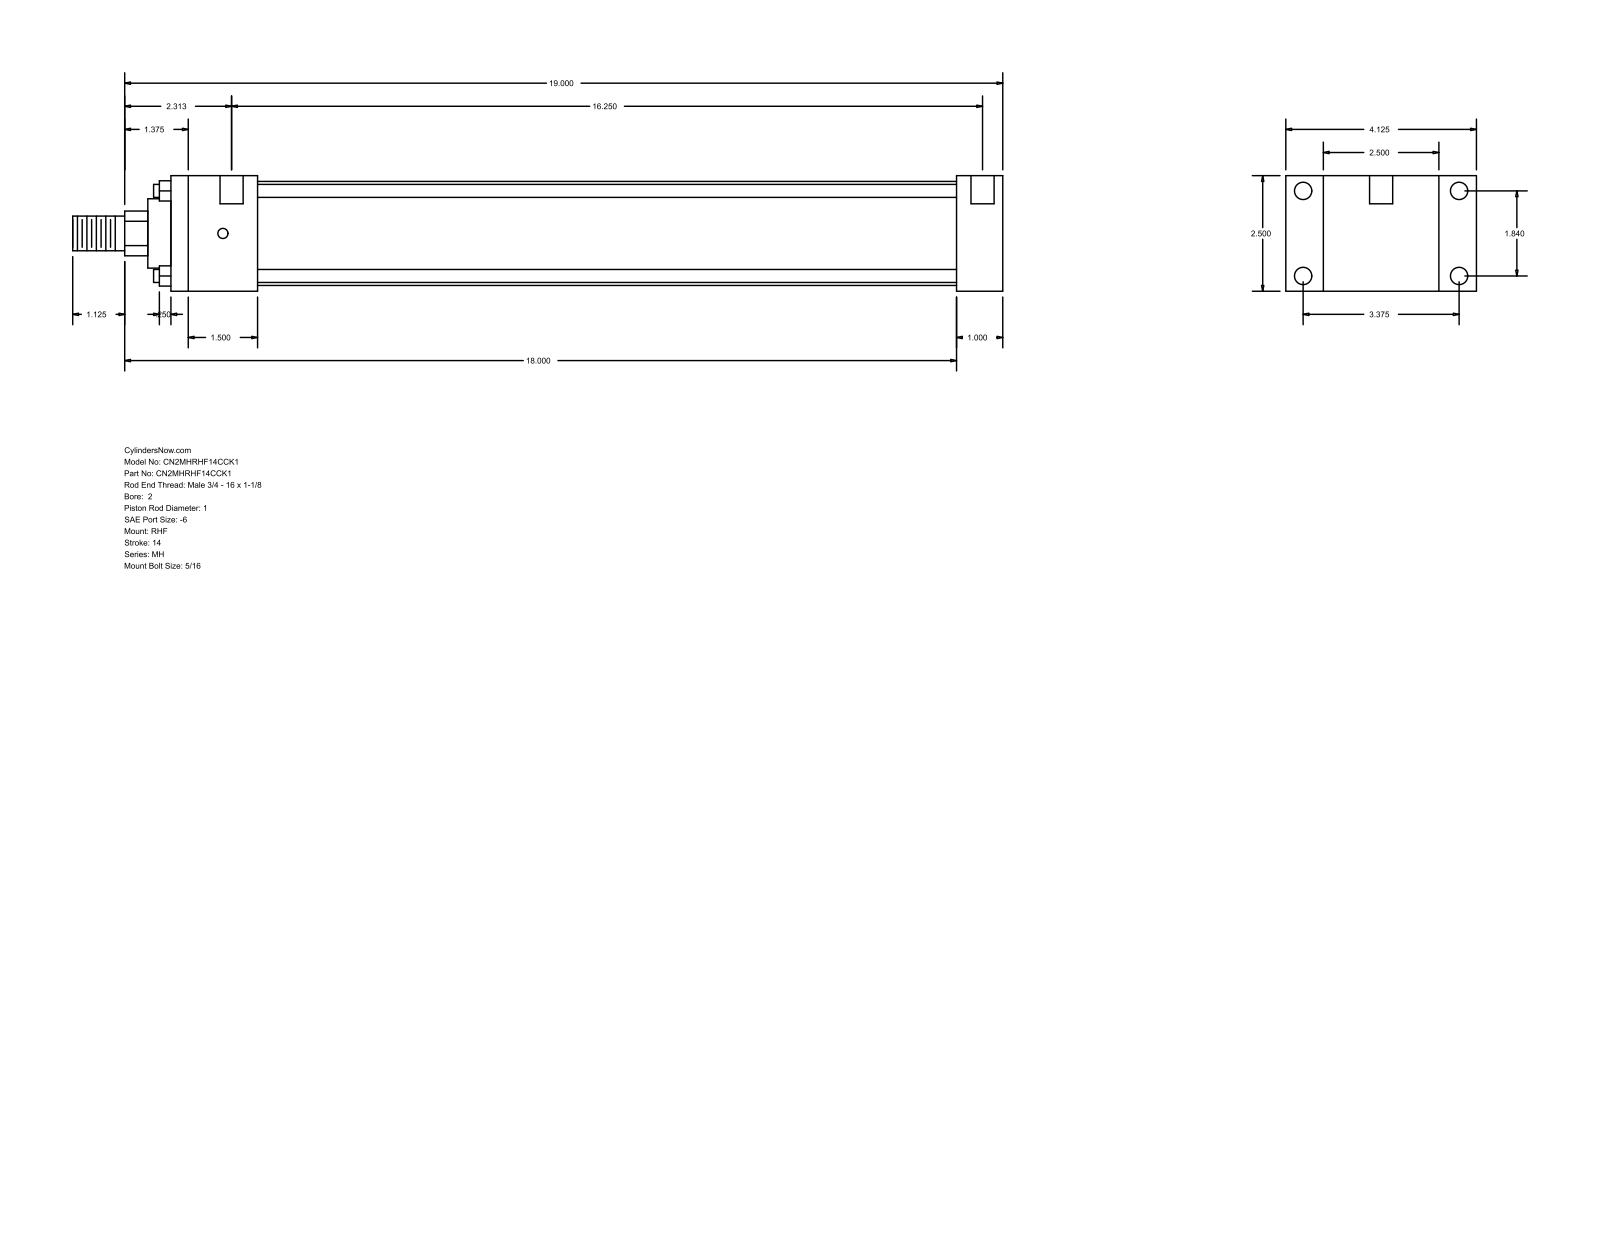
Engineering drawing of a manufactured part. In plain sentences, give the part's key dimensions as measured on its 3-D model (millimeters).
The part is named "MH_RHF__0200_1". Its 3-D file was written by "GSSL Pune (CONFIG_CONTROL_DESIGN)". It is 0 solids with 88 faces: 60 planar, 28 cylindrical and 0 other. Overall it measures 511.18 by 104.78 by 63.5 millimeters. Round holes: 4 of diameter 5.56, 4 of diameter 9.53, 2 of diameter 12.7. Round bosses or shafts: 4 of diameter 7.14, 1 of diameter 57.15, 1 of diameter 38.1, 1 of diameter 25.4, 1 of diameter 19.05. Partial cylindrical surfaces (rounded edges, fillets, slot ends): 1 of radius 12.29. The main face-to-face distances are 63.5, 25.4, 20.64, 84.14, 457.2, 431.8, 104.78, 47.63, 384.17, 409.57. The hole center spacings are 46.74, 85.72, 97.63, 420.68, 3.17, 4.76, 412.75, 415.92.
